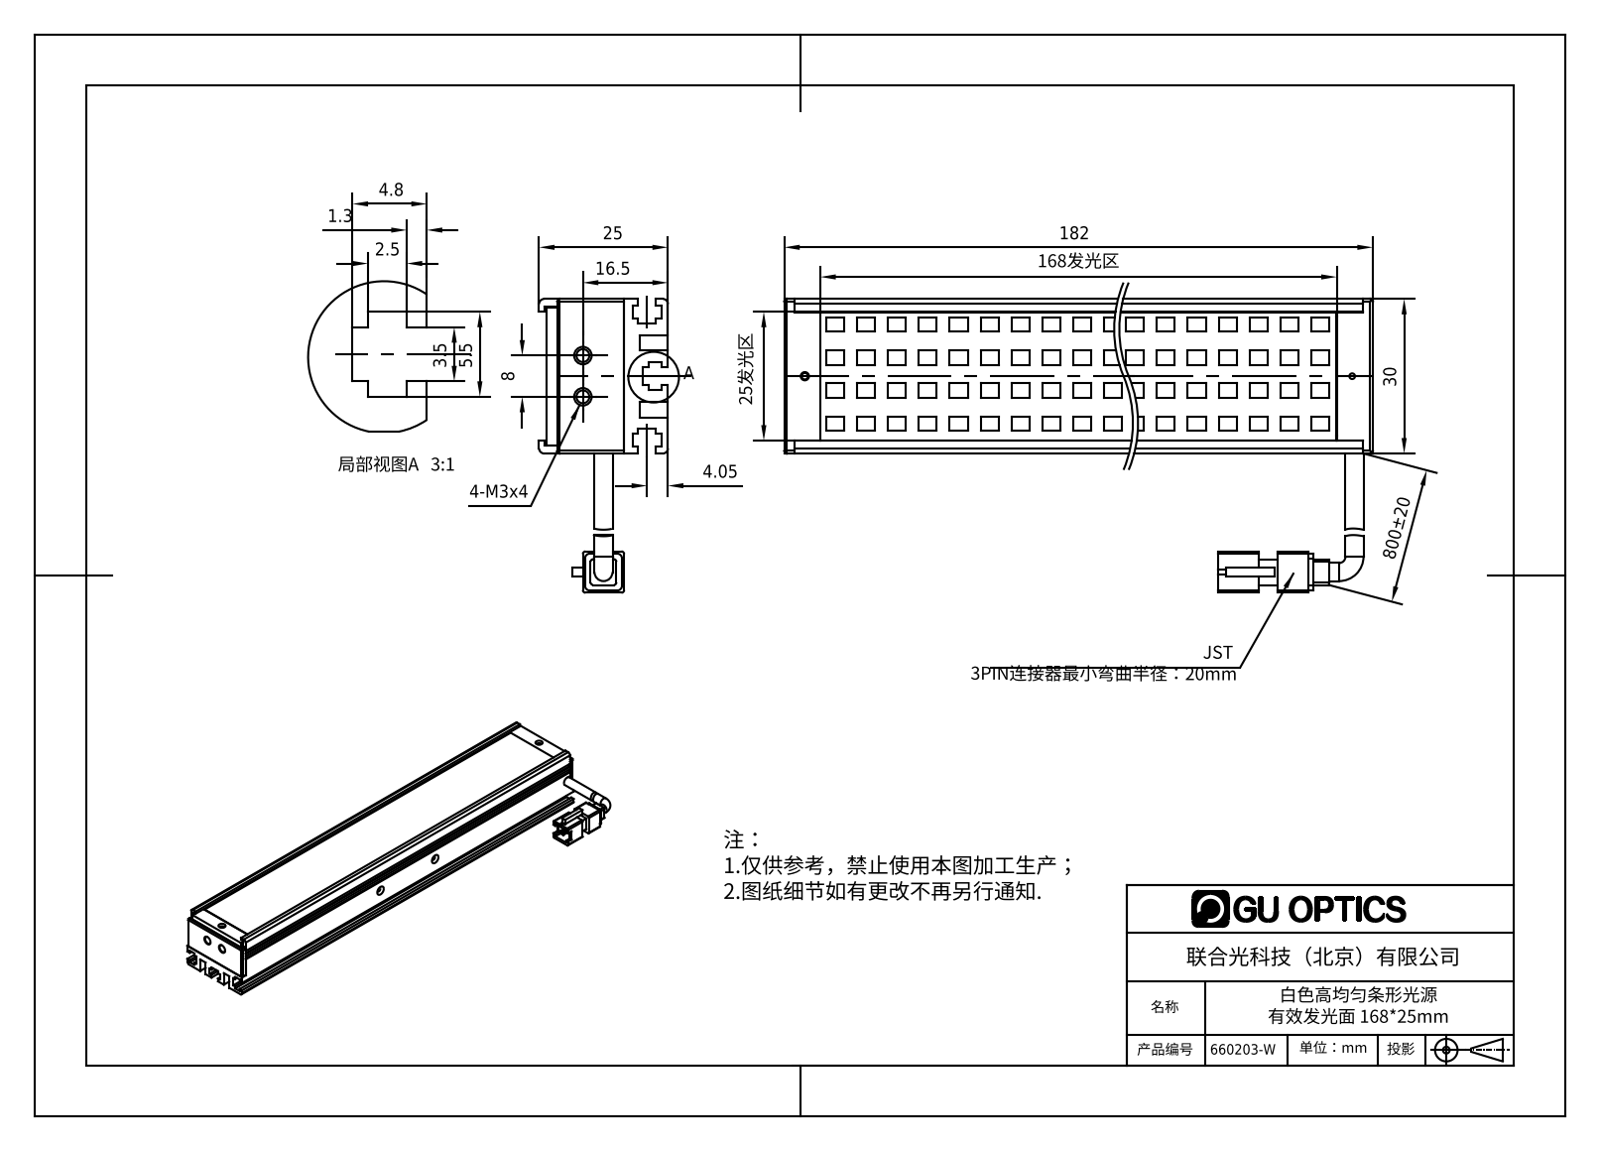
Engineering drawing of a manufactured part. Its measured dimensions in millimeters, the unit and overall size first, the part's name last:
Units: millimetres
Overall size (bounding box): 182 × 57 × 25
Round holes (diameter × count): ⌀1.6 ×5, ⌀1.5 ×2, ⌀1.7 ×2, ⌀2.5 ×2, ⌀2.8 ×2, ⌀3 ×2, ⌀1.1 ×1, ⌀1.25 ×1, ⌀2 ×1
Round bosses / shafts (diameter × count): ⌀3.5 ×2
Partial cylindrical surfaces — rounded edges, fillets, slot ends (radius × count): R1 ×12, R0.5 ×8, R1.65 ×1
Main face-to-face distances: 1, 13, 2, 2.5, 3, 9.5, 27.5, 4.5, 12, 8.5
Hole centre spacings: 174, 7, 72, 72.3, 102, 102.21, 174.14, 8
Volume: 63 499 mm³ · Surface area: 64 448 mm²
Bodies: 6 solids, 1004 faces (818 planar, 83 cylindrical, 103 other)
Part name (STEP PRODUCT): 660203-W
STEP written by: SolidWorks 2016 (AUTOMOTIVE_DESIGN)
